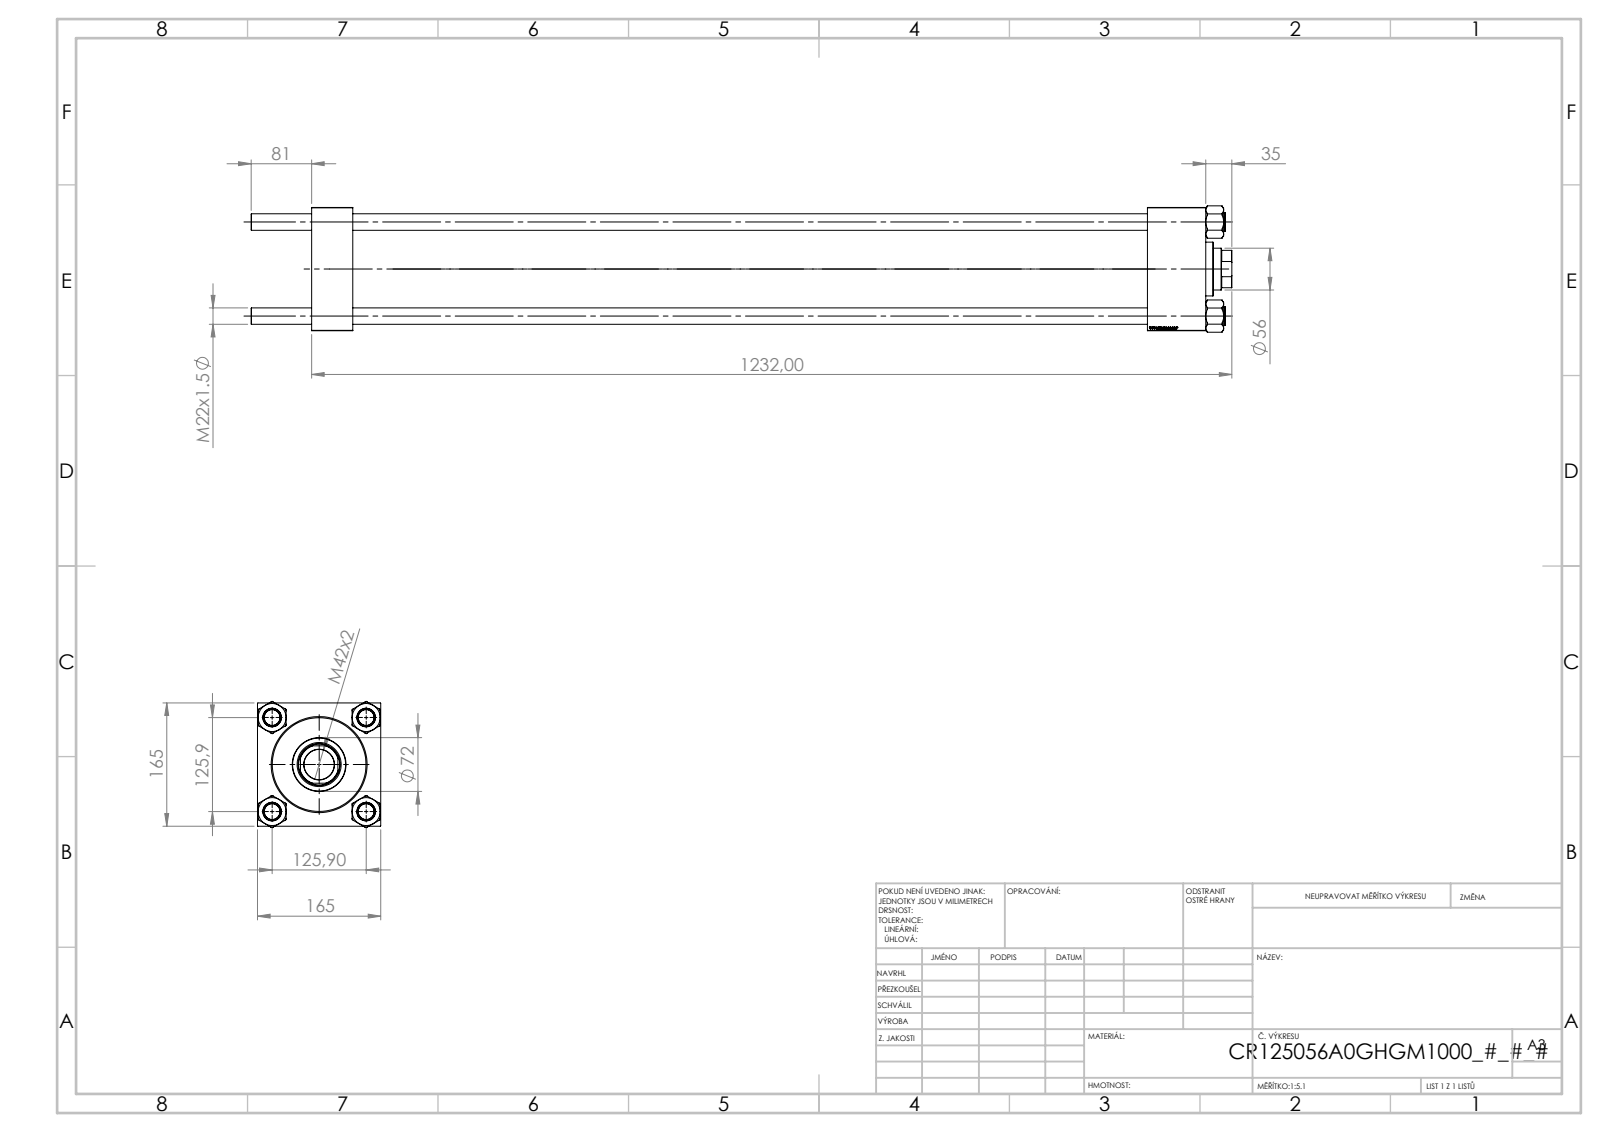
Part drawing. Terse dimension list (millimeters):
name: V215CR_VCP; V215_VC_A; V215CR_BODY_A; CR025_012_A_0_G_A_G_M_020_+#_##_TYCINKA (+1 more)
written by: SolidWorks 2019 (CONFIG_CONTROL_DESIGN)
unit: mm
bodies: 11 solids, 1182 faces (568 planar, 78 cylindrical, 536 other)
size: 1313 × 169.14 × 165
volume: 9 767 000 mm³; area: 1 780 000 mm²
holes: 4× ⌀22, 2× ⌀7, 2× ⌀32.24, 2× ⌀45, 1× ⌀40.5, 1× ⌀56, 1× ⌀59, 1× ⌀96, 1× ⌀125, 1× ⌀125.5
bosses: 4× ⌀25, 1× ⌀131, 1× ⌀72
rounds: 1× R27
face distances: 165, 55, 1197, 1142, 1119, 1064, 78, 1168.3, 1113.3, 49.3
hole spacings: 89.02, 125.9, 178.05, 1118.5
